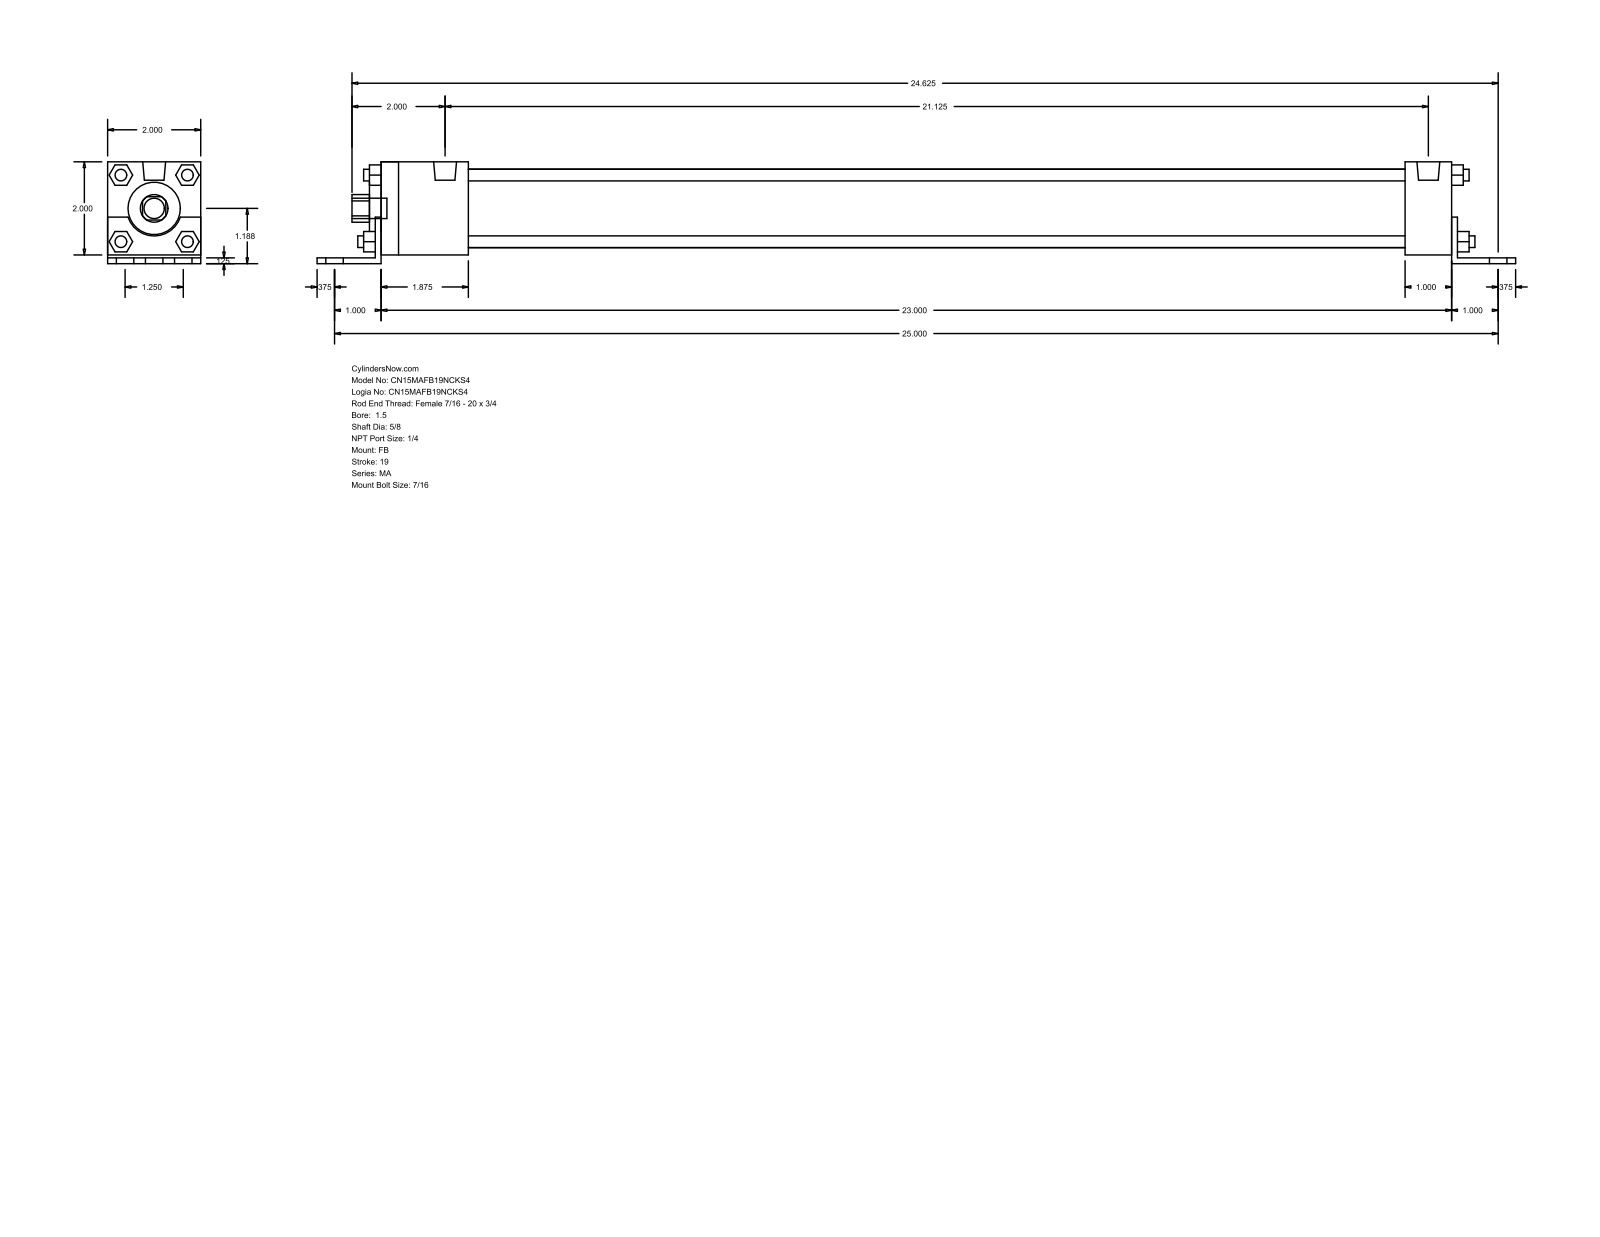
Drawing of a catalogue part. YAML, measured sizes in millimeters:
part_name: "MA_FB__0150_0.625"
step_written_by: "GSSL Pune (CONFIG_CONTROL_DESIGN)"
units: millimeters
bodies: {solids: 0, faces: 140, planar: 105, cylindrical: 35, other: 0}
overall_size: [654.05, 55.56, 50.8]
round_holes:
  - {diameter: 15.88, count: 1}
  - {diameter: 28.57, count: 1}
  - {diameter: 42.93, count: 1}
round_bosses_or_shafts:
  - {diameter: 11.11, count: 7}
  - {diameter: 7.94, count: 4}
  - {diameter: 6.35, count: 4}
  - {diameter: 12.49, count: 2}
partial_cylinders:
  - {radius: 7.54, count: 1}
  - {radius: 15.05, count: 1}
face_to_face_distances: [50.8, 3.17, 4.76, 55.56, 1.59, 52.39, 590.55, 6.35, 584.2, 28.58]
